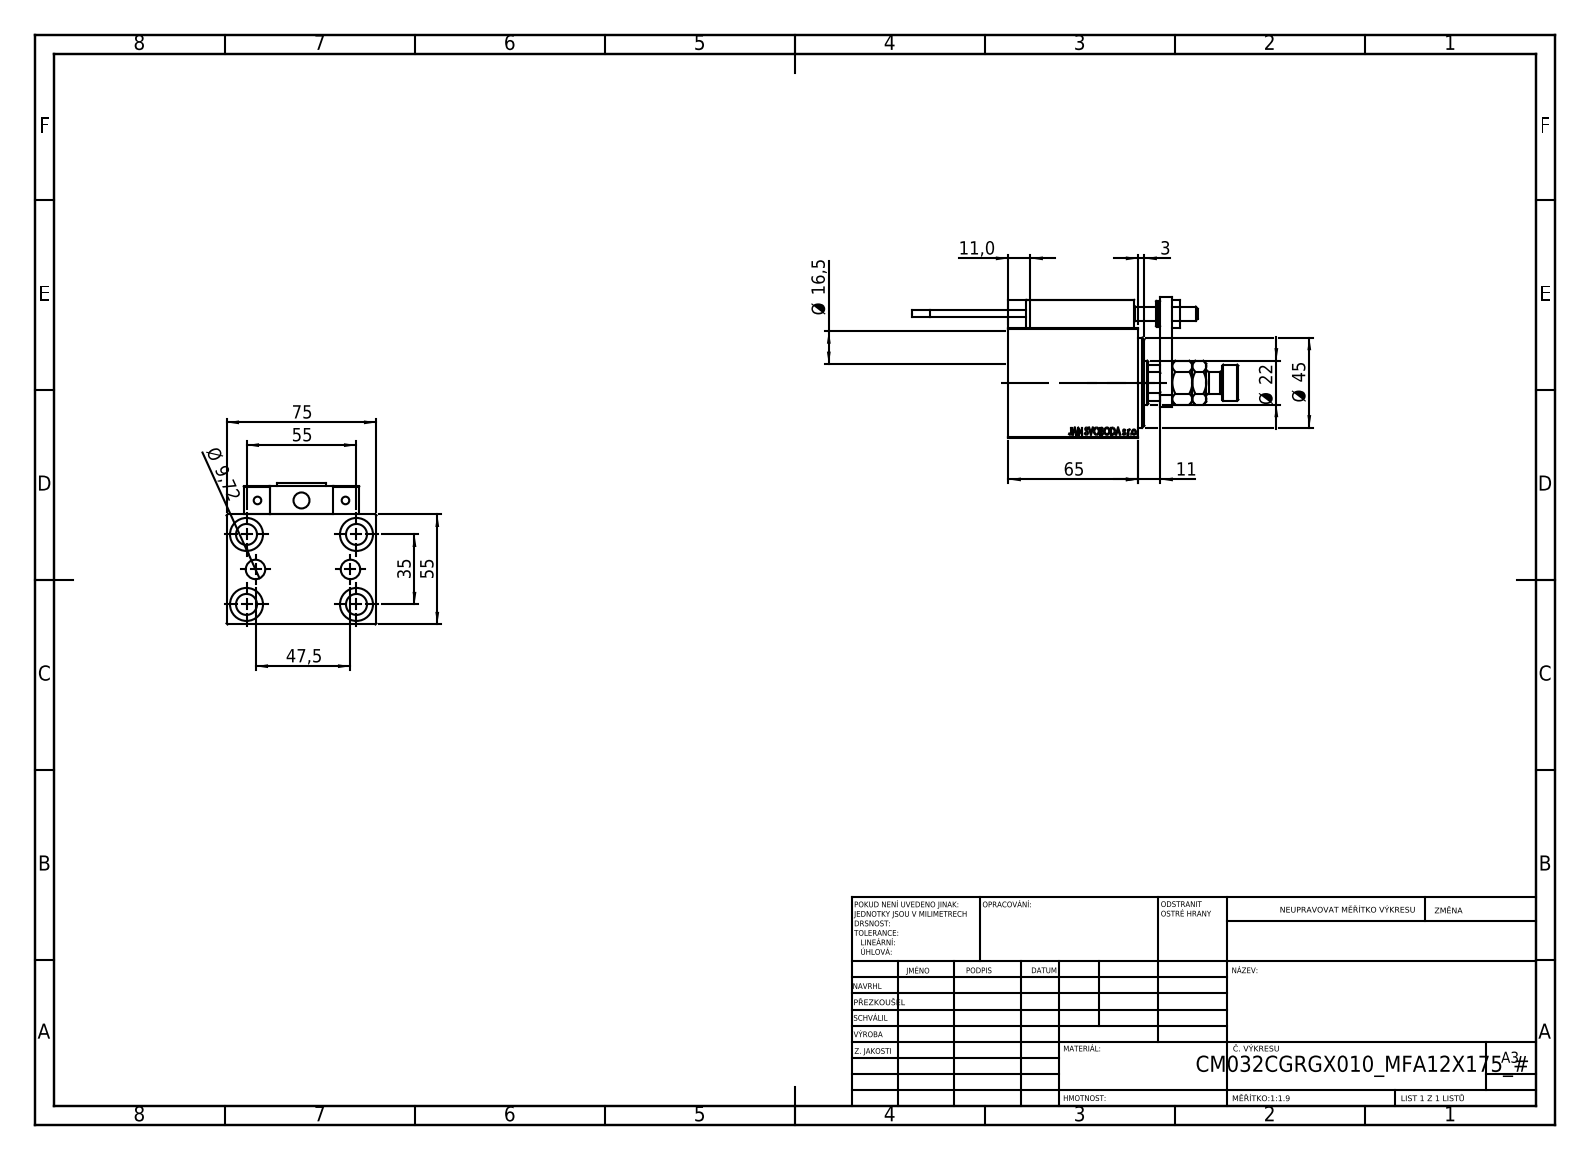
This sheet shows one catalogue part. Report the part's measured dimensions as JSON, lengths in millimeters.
{"part_name": "ALLEN BOLT D5; SWITCH_X_FRONT_BACK; SWITCH X; NUT_D12 (+8 more)", "step_written_by": "SolidWorks 2019 (CONFIG_CONTROL_DESIGN)", "units": "millimeters", "bodies": {"solids": 24, "faces": 1324, "planar": 574, "cylindrical": 184, "other": 566}, "overall_size": [163, 75, 70.5], "volume_mm3": 289156, "surface_area_mm2": 81281, "round_holes": [[8, 5], [10.5, 5], [16.5, 5], [3.2, 4], [4, 4], [5, 2], [9.72, 2], [7, 1], [22, 1], [25.5, 1], [32, 1], [34, 1]], "round_bosses_or_shafts": [[11, 2], [5, 2], [3.8, 2], [18, 1], [13, 1]], "partial_cylinders_radius": [[0.3, 30], [3, 2], [10.5, 1]], "face_to_face_distances": [55, 14, 75, 11, 3, 22, 54, 68, 65, 69], "hole_center_spacings": [32.6, 11.37, 17.12, 17.76, 18.07, 20, 27.8, 29.59]}
